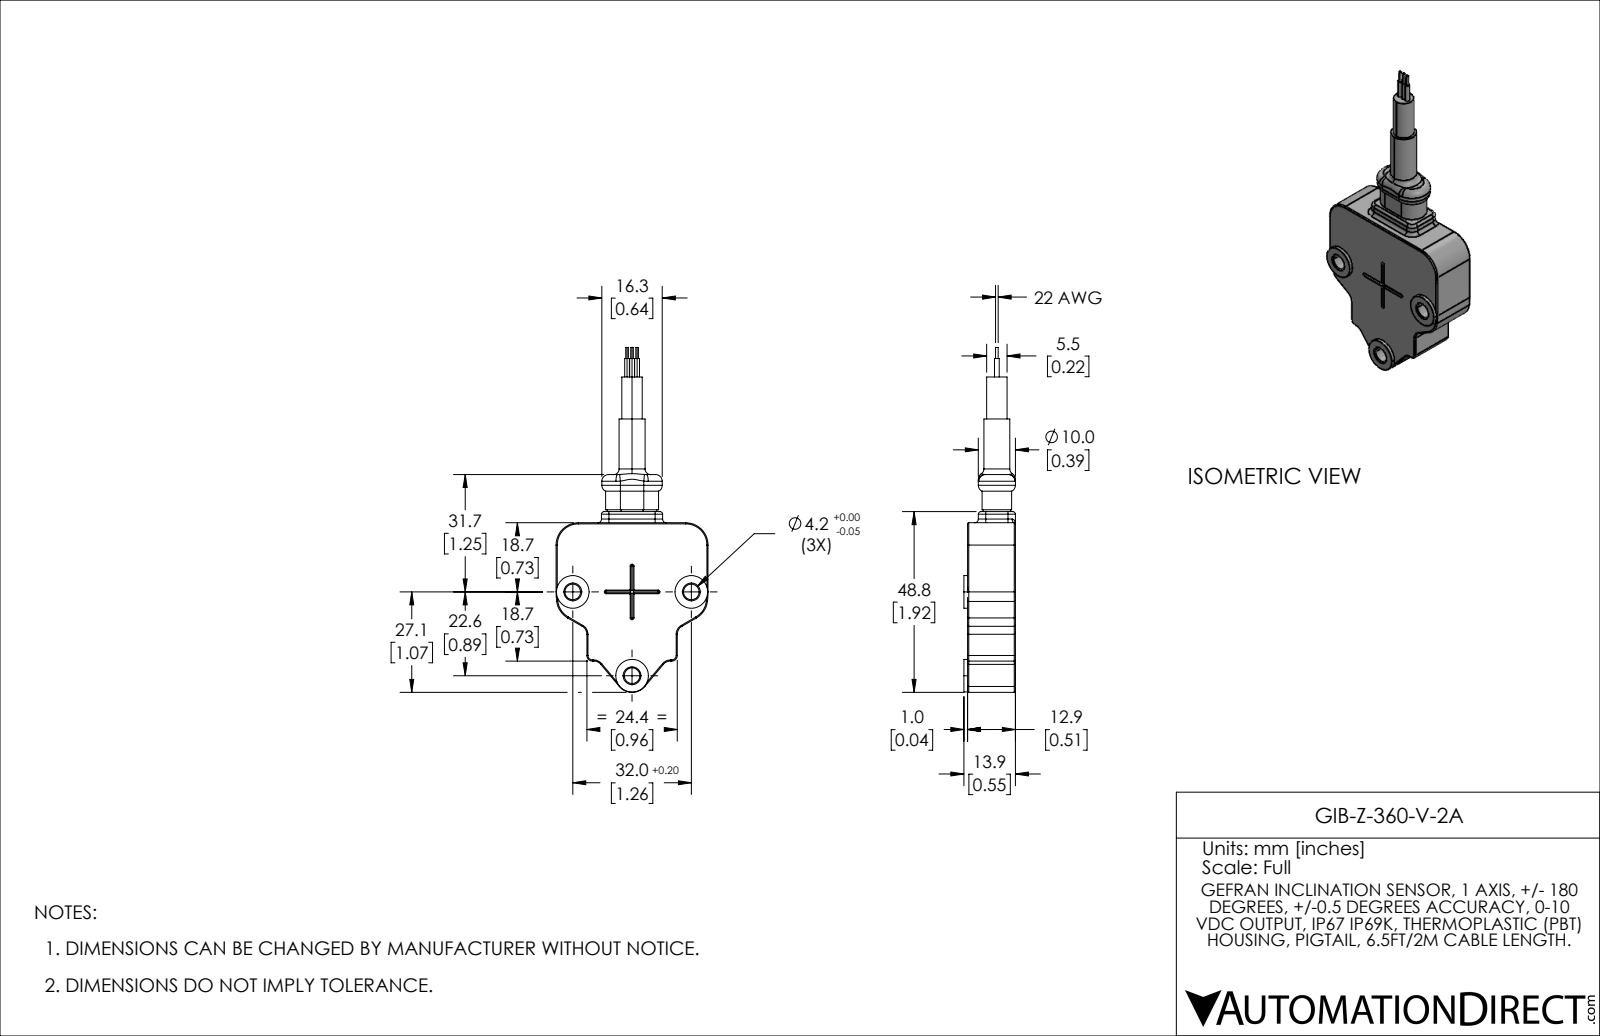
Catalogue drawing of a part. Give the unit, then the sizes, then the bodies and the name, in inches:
Units: inches
Overall size (bounding box): 3.663 × 1.614 × 0.547
Round holes (diameter × count): ⌀0.165 ×3
Round bosses / shafts (diameter × count): ⌀0.346 ×3, ⌀0.051 ×3, ⌀0.028 ×3, ⌀0.276 ×1, ⌀0.217 ×1
Partial cylindrical surfaces — rounded edges, fillets, slot ends (radius × count): R0.012 ×20, R0.008 ×4, R0.028 ×4, R0.079 ×4, R0.098 ×4, R0.236 ×4, R0.039 ×3, R0.059 ×2
Main face-to-face distances: 0.508, 0.039, 1.614, 0.327, 1.287, 0.547, 0.961, 0.354, 0.154, 0.118
Hole centre spacings: 1.09, 1.26
Volume: 1.246 in³ · Surface area: 9.975 in²
Bodies: 1 solid, 201 faces (47 planar, 87 cylindrical, 67 other)
Part name (STEP PRODUCT): GIB-Z-360-V-2A
STEP written by: SolidWorks 2021 (AUTOMOTIVE_DESIGN)
